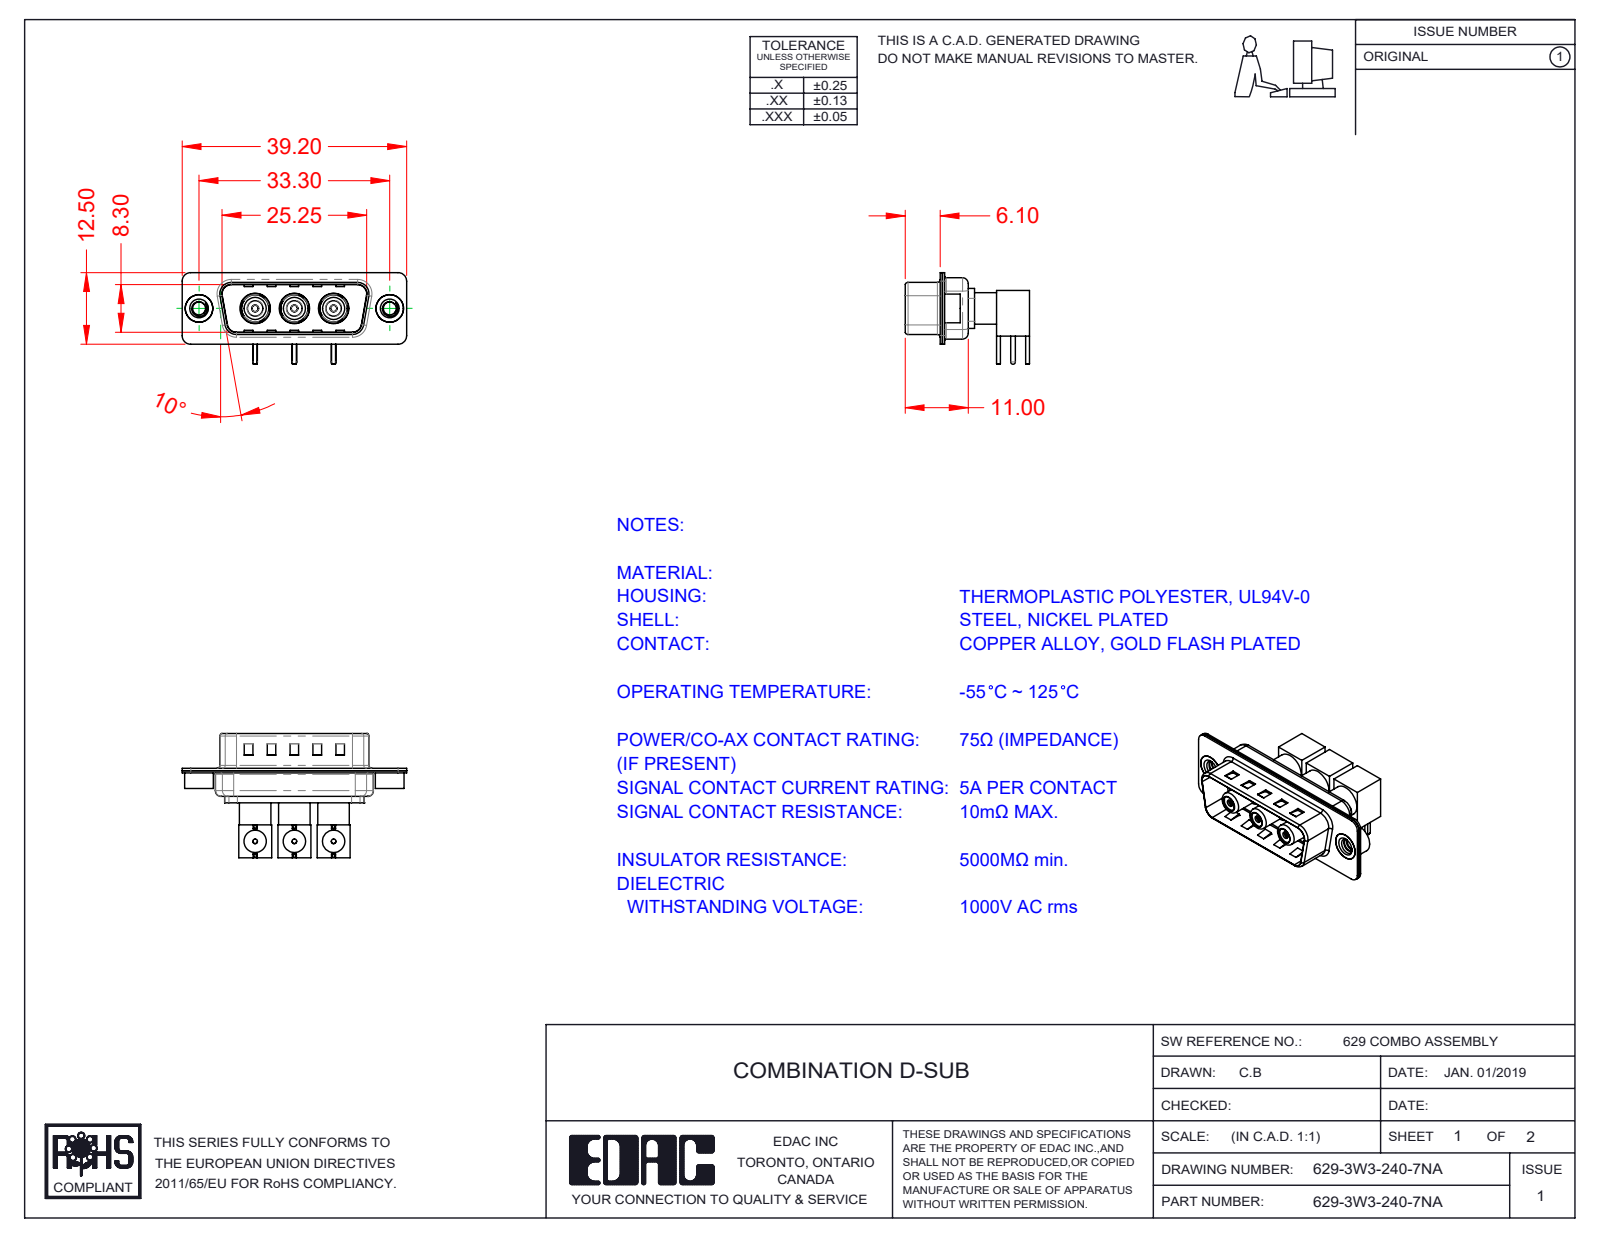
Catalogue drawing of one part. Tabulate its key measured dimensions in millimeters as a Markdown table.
| quantity | value |
| --- | --- |
| part name | Insulator Socket 2; Locking Collar; Socket_RA; RA Back Shell (+8 more) |
| STEP written by | SolidWorks 2020 (CONFIG_CONTROL_DESIGN) |
| units | millimeters |
| bodies | 26 solids, 796 faces (310 planar, 334 cylindrical, 152 other) |
| overall size | 39.2 × 21.71 × 16 |
| volume | 2 698 mm³ |
| surface area | 7 523 mm² |
| round holes (diameter × count) | 0.8 × 3, 1.1 × 3, 1.2 × 3, 1.5 × 3, 1.6 × 3, 2.5 × 3, 2.7 × 3, 3.1 × 3, 3.4 × 3, 3.9 × 3, 4.1 × 3, 4.85 × 3 |
| round bosses / shafts (diameter × count) | 0.8 × 6, 5.5 × 3, 5.2 × 3, 4.8 × 3, 4.73 × 3, 4.16 × 3, 4 × 3, 3.85 × 3 |
| partial cylindrical surfaces (radius × count) | 1.5 × 16, 2 × 12, 0.5 × 8, 1.6 × 8, 0.25 × 4, 0.6 × 4, 0.65 × 4, 0.9 × 4 |
| main face-to-face distances | 0.4, 0.8, 5.75, 9.5, 0.35, 6.85, 9.1, 8.7, 1.4, 9.9 |
| hole center spacings | 6.85, 13.7, 9.8, 16.65, 23.5, 33.3 |
